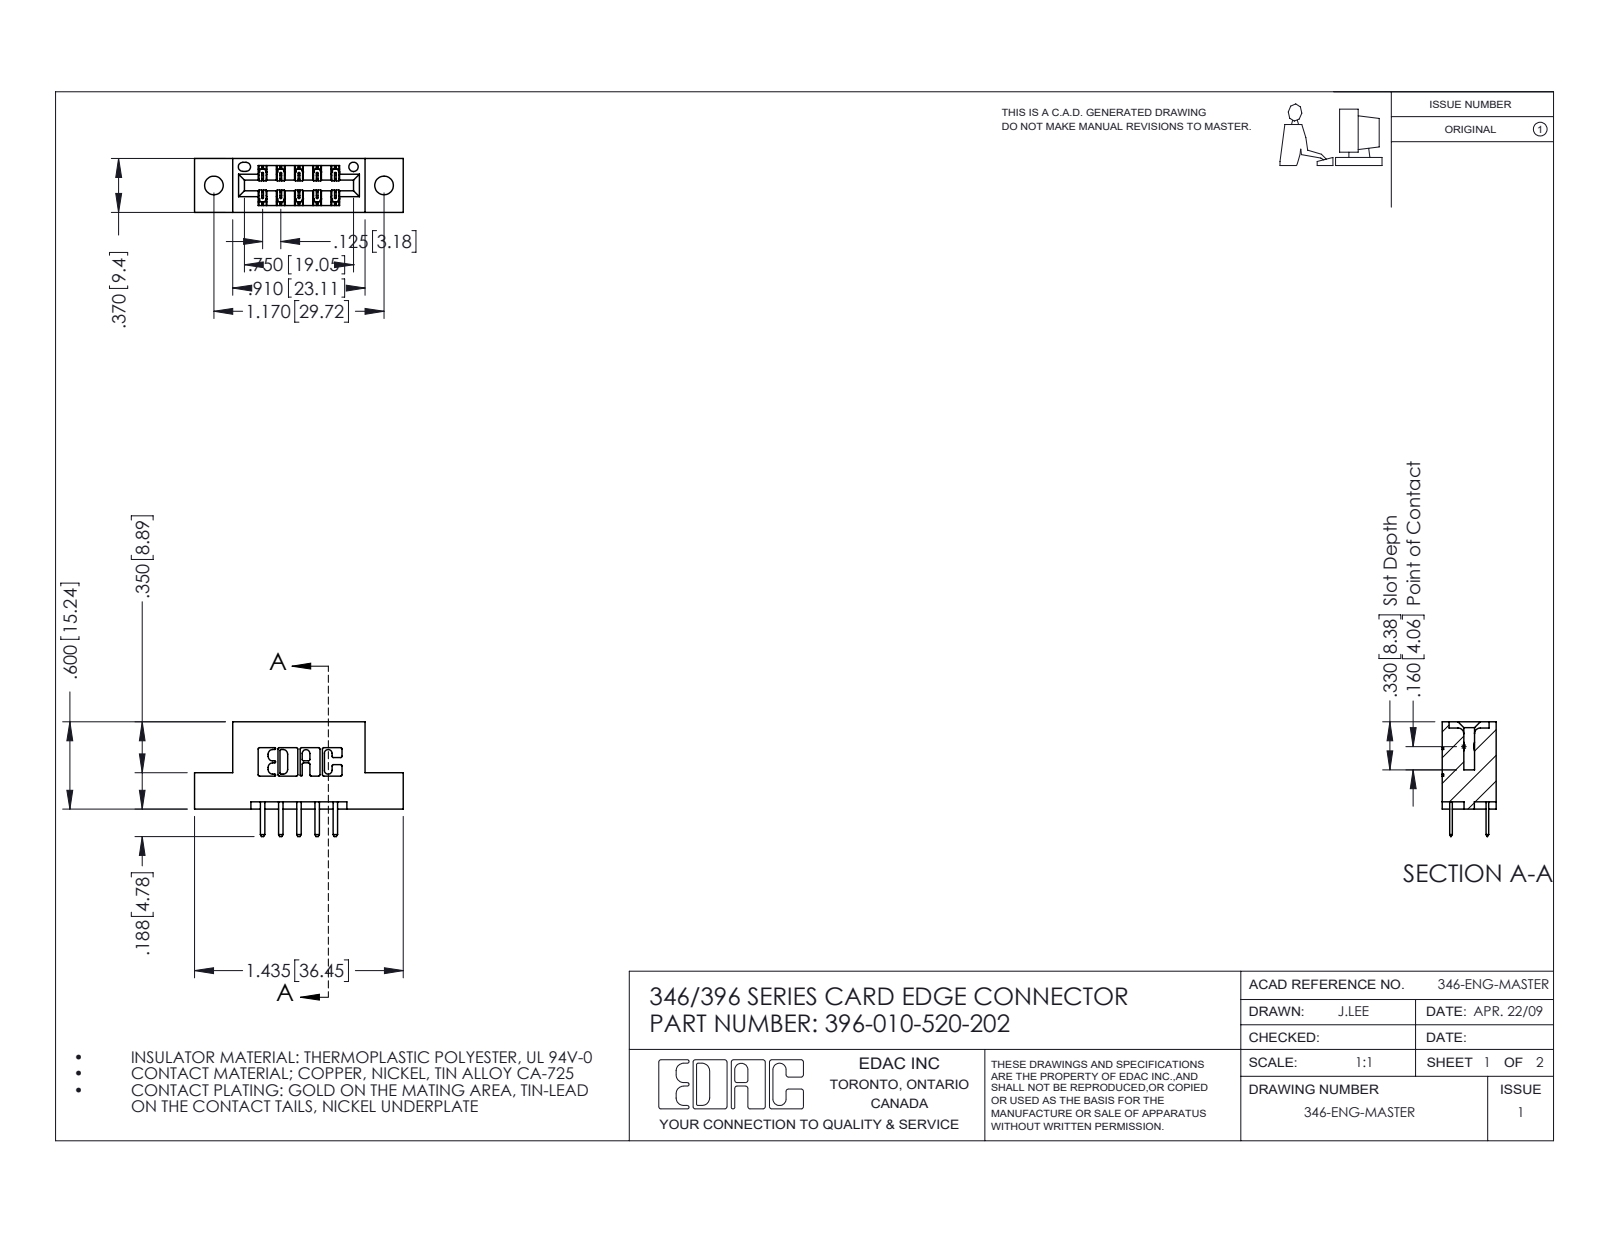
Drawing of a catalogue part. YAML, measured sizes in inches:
part_name: "396-010-520-202; 346 Part_Flush Mounting Lugs - 0.128 Dia; 345-292-001_345-293-120"
step_written_by: "SolidWorks 2016 (CONFIG_CONTROL_DESIGN)"
units: inches
bodies: {solids: 11, faces: 682, planar: 446, cylindrical: 236, other: 0}
overall_size: [1.435, 0.788, 0.37]
volume: 0.197
surface_area: 5.538
round_holes:
  - {diameter: 0.128, count: 2}
  - {diameter: 0.064, count: 1}
partial_cylinders:
  - {radius: 0.01, count: 22}
  - {radius: 0.006, count: 15}
  - {radius: 0.01, count: 14}
  - {radius: 0.007, count: 6}
  - {radius: 0.031, count: 6}
  - {radius: 0.026, count: 3}
  - {radius: 0.014, count: 2}
  - {radius: 0.022, count: 2}
face_to_face_distances: [0.25, 0.37, 0.048, 0.322, 0.148, 0.222, 0.1, 0.174, 0.125, 0.275]
hole_center_spacings: [0.246, 0.969, 1.17]
